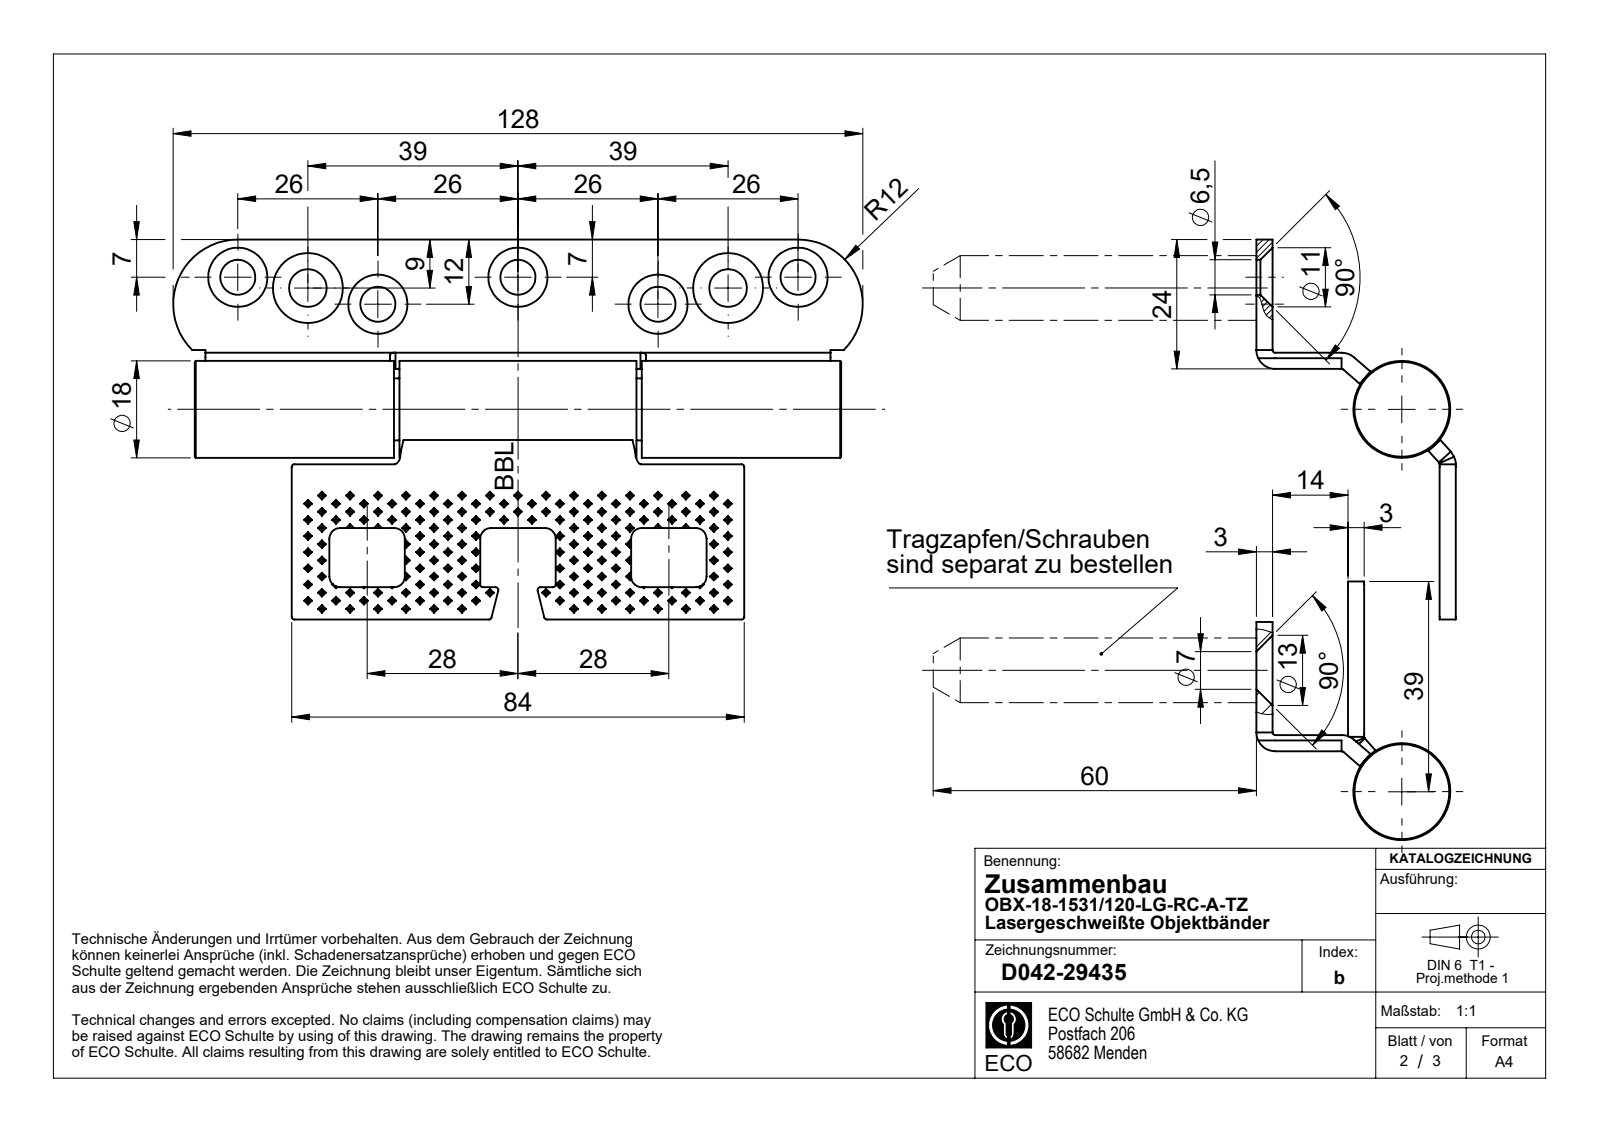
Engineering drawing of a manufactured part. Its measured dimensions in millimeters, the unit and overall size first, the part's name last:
Units: millimetres
Overall size (bounding box): 128 × 96 × 48
Round holes (diameter × count): ⌀6.5 ×5, ⌀2 ×2, ⌀5 ×2, ⌀0.5 ×1, ⌀4.5 ×1, ⌀7.9 ×1
Round bosses / shafts (diameter × count): ⌀12 ×3, ⌀6 ×2, ⌀18 ×1, ⌀11.8 ×1, ⌀11.5 ×1, ⌀7.7 ×1, ⌀4 ×1, ⌀1.65 ×1
Partial cylindrical surfaces — rounded edges, fillets, slot ends (radius × count): R0.5 ×13, R2 ×10, R0.25 ×6, R3.5 ×3, R0.68 ×2, R2.1 ×2, R3 ×2, R12 ×2
Main face-to-face distances: 3, 17, 20, 14, 11.5, 82, 25.5, 108.5, 21, 24
Hole centre spacings: 26.48, 52, 13.15, 13.34, 39.05, 65.07, 78.16, 91.02
Volume: 61 833 mm³ · Surface area: 36 585 mm²
Bodies: 15 solids, 1896 faces (1620 planar, 149 cylindrical, 127 other)
Part name (STEP PRODUCT): D044-14308; DIN5401-III; D046-14312; ISO 10642_M6x16 - A2-70 (+6 more)
STEP written by: SolidWorks 2020 (CONFIG_CONTROL_DESIGN)
